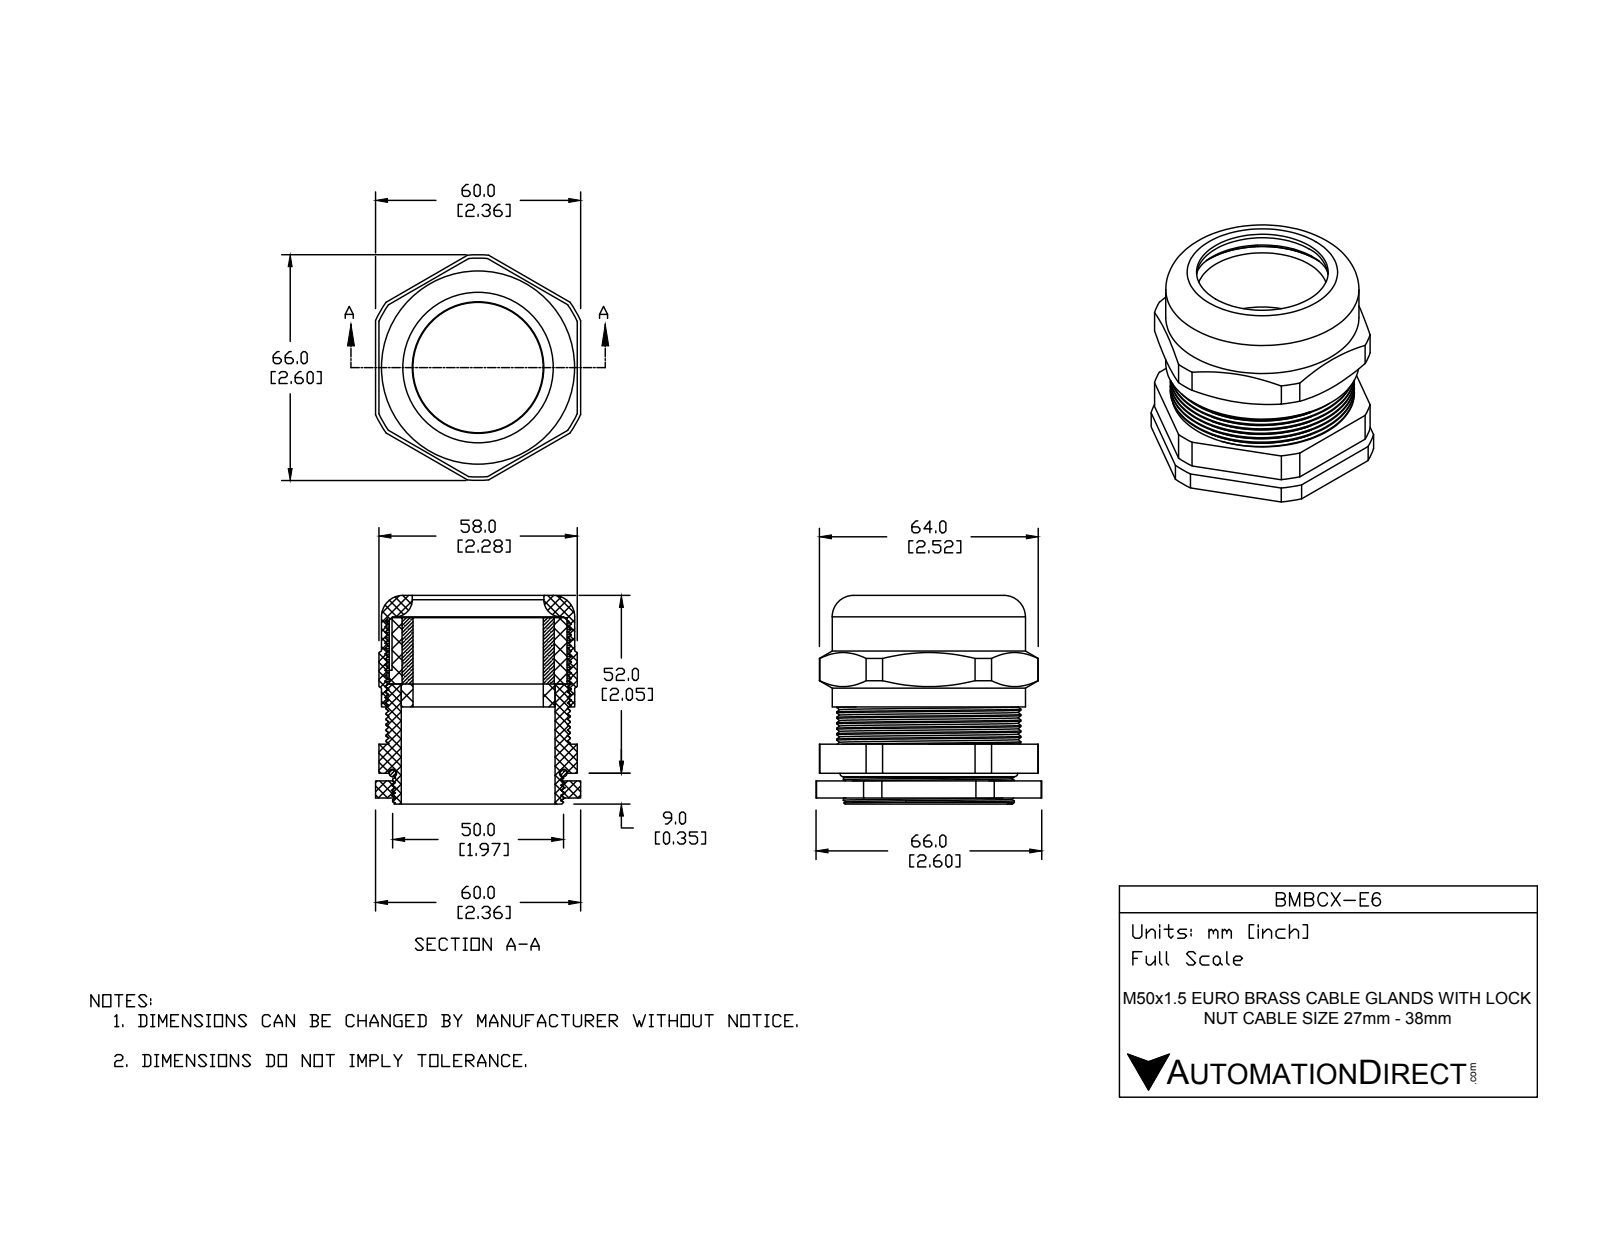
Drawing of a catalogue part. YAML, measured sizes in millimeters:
part_name: "BMBCX-E6"
step_written_by: "SolidWorks 2015 (CONFIG_CONTROL_DESIGN)"
units: millimeters
bodies: {solids: 6, faces: 279, planar: 133, cylindrical: 115, other: 31}
overall_size: [66, 61, 60]
volume: 68765
surface_area: 55065
round_holes:
  - {diameter: 38.1, count: 1}
  - {diameter: 38.5, count: 1}
  - {diameter: 44.5, count: 1}
  - {diameter: 45, count: 1}
  - {diameter: 49.19, count: 1}
  - {diameter: 53.04, count: 1}
round_bosses_or_shafts:
  - {diameter: 56.5, count: 1}
  - {diameter: 53.8, count: 1}
  - {diameter: 52, count: 1}
  - {diameter: 50, count: 1}
partial_cylinders:
  - {radius: 32, count: 1}
  - {radius: 33, count: 1}
face_to_face_distances: [19.4, 0.5, 26.1, 58, 33.35, 5, 28.35, 52.75, 47.75, 1]
